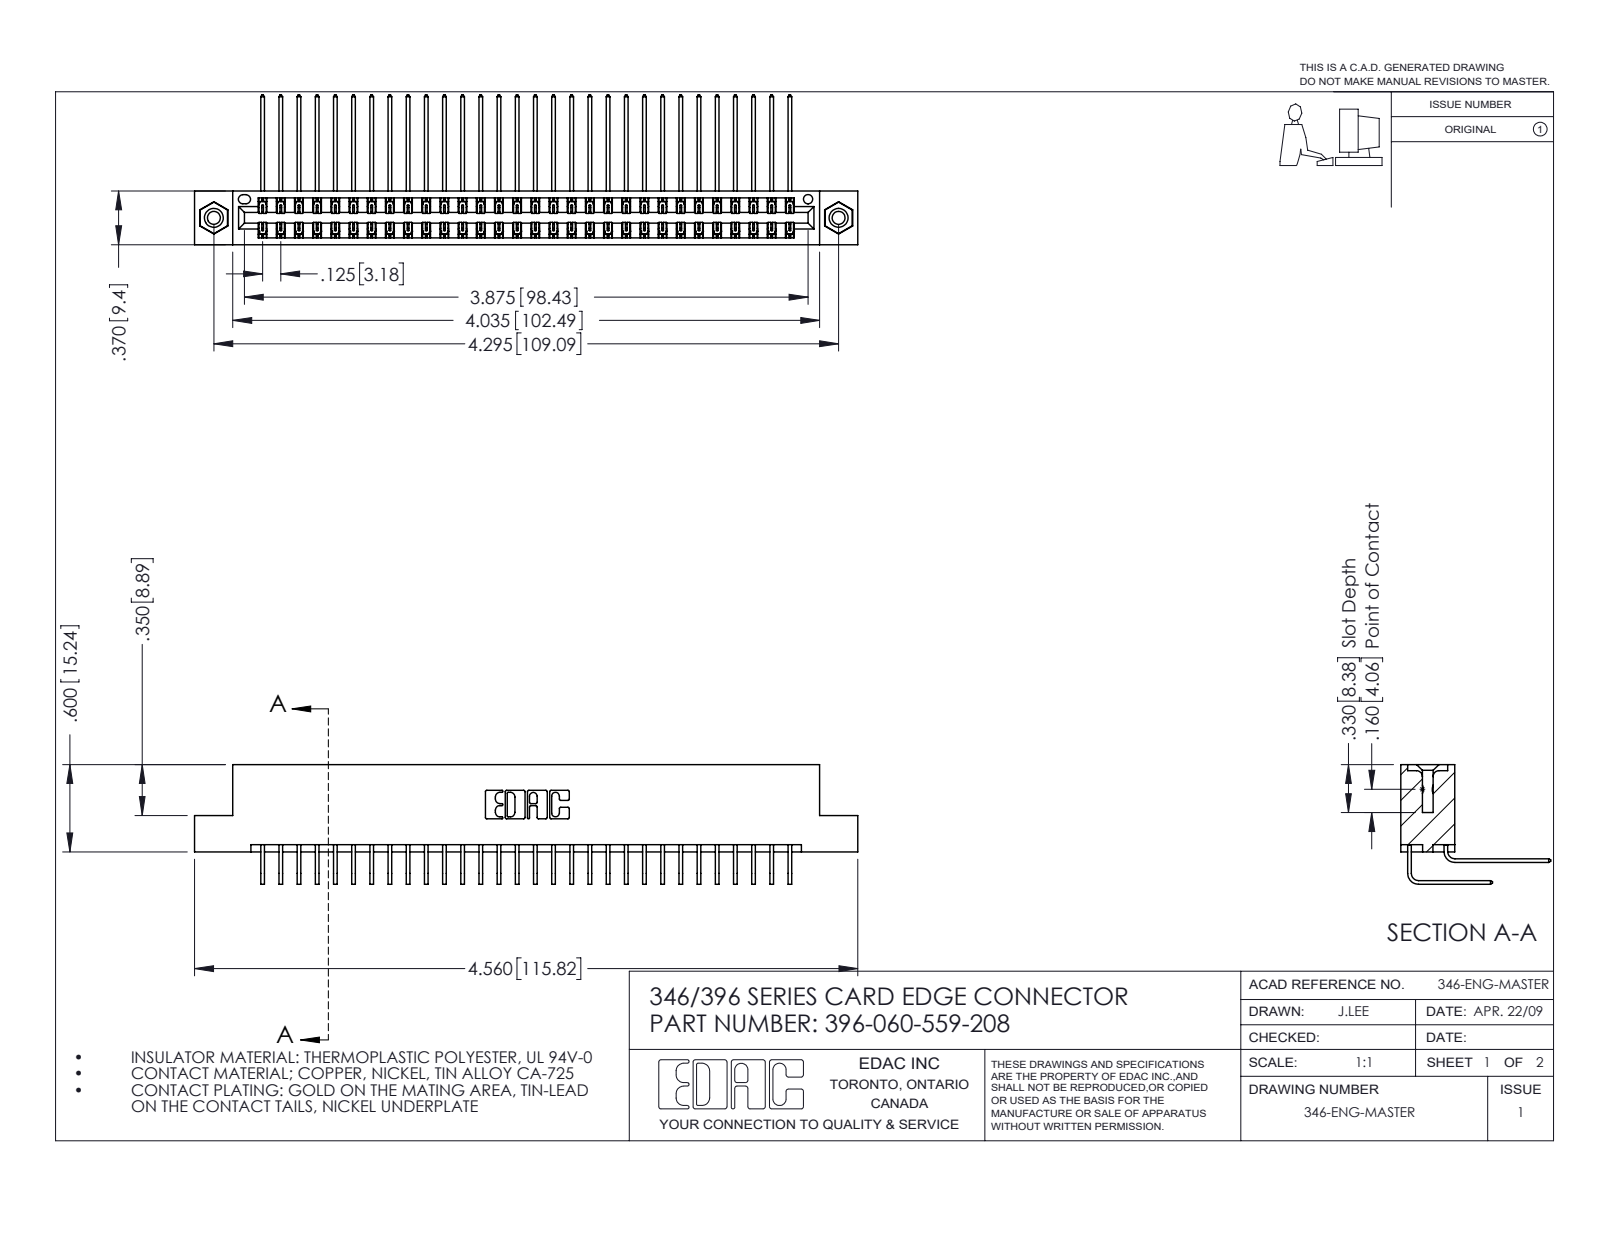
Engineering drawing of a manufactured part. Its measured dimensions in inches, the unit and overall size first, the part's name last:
Units: inches
Overall size (bounding box): 4.56 × 1.03 × 0.823
Round holes (diameter × count): ⌀0.089 ×2, ⌀0.125 ×2, ⌀0.156 ×2, ⌀0.064 ×1
Round bosses / shafts (diameter × count): ⌀0.155 ×2
Partial cylindrical surfaces — rounded edges, fillets, slot ends (radius × count): R0.006 ×90, R0.01 ×22, R0.007 ×6, R0.031 ×6, R0.026 ×3, R0.014 ×2, R0.022 ×2, R0.024 ×2
Main face-to-face distances: 0.048, 0.322, 0.025, 0.25, 0.37, 0.072, 0.298, 0.275, 0.148, 0.222
Hole centre spacings: 0.246, 4.087, 4.295
Volume: 0.704 in³ · Surface area: 26.9 in²
Bodies: 63 solids, 3422 faces (2328 planar, 1078 cylindrical, 16 other)
Part name (STEP PRODUCT): 346 Part_Flush Mounting Lugs - 0.156 Dia-TI; 345-250-001_345-250-003-102; 396-060-559-208; 345-292-001_559 Tail - 2 (+1 more)
STEP written by: SolidWorks 2016 (CONFIG_CONTROL_DESIGN)
